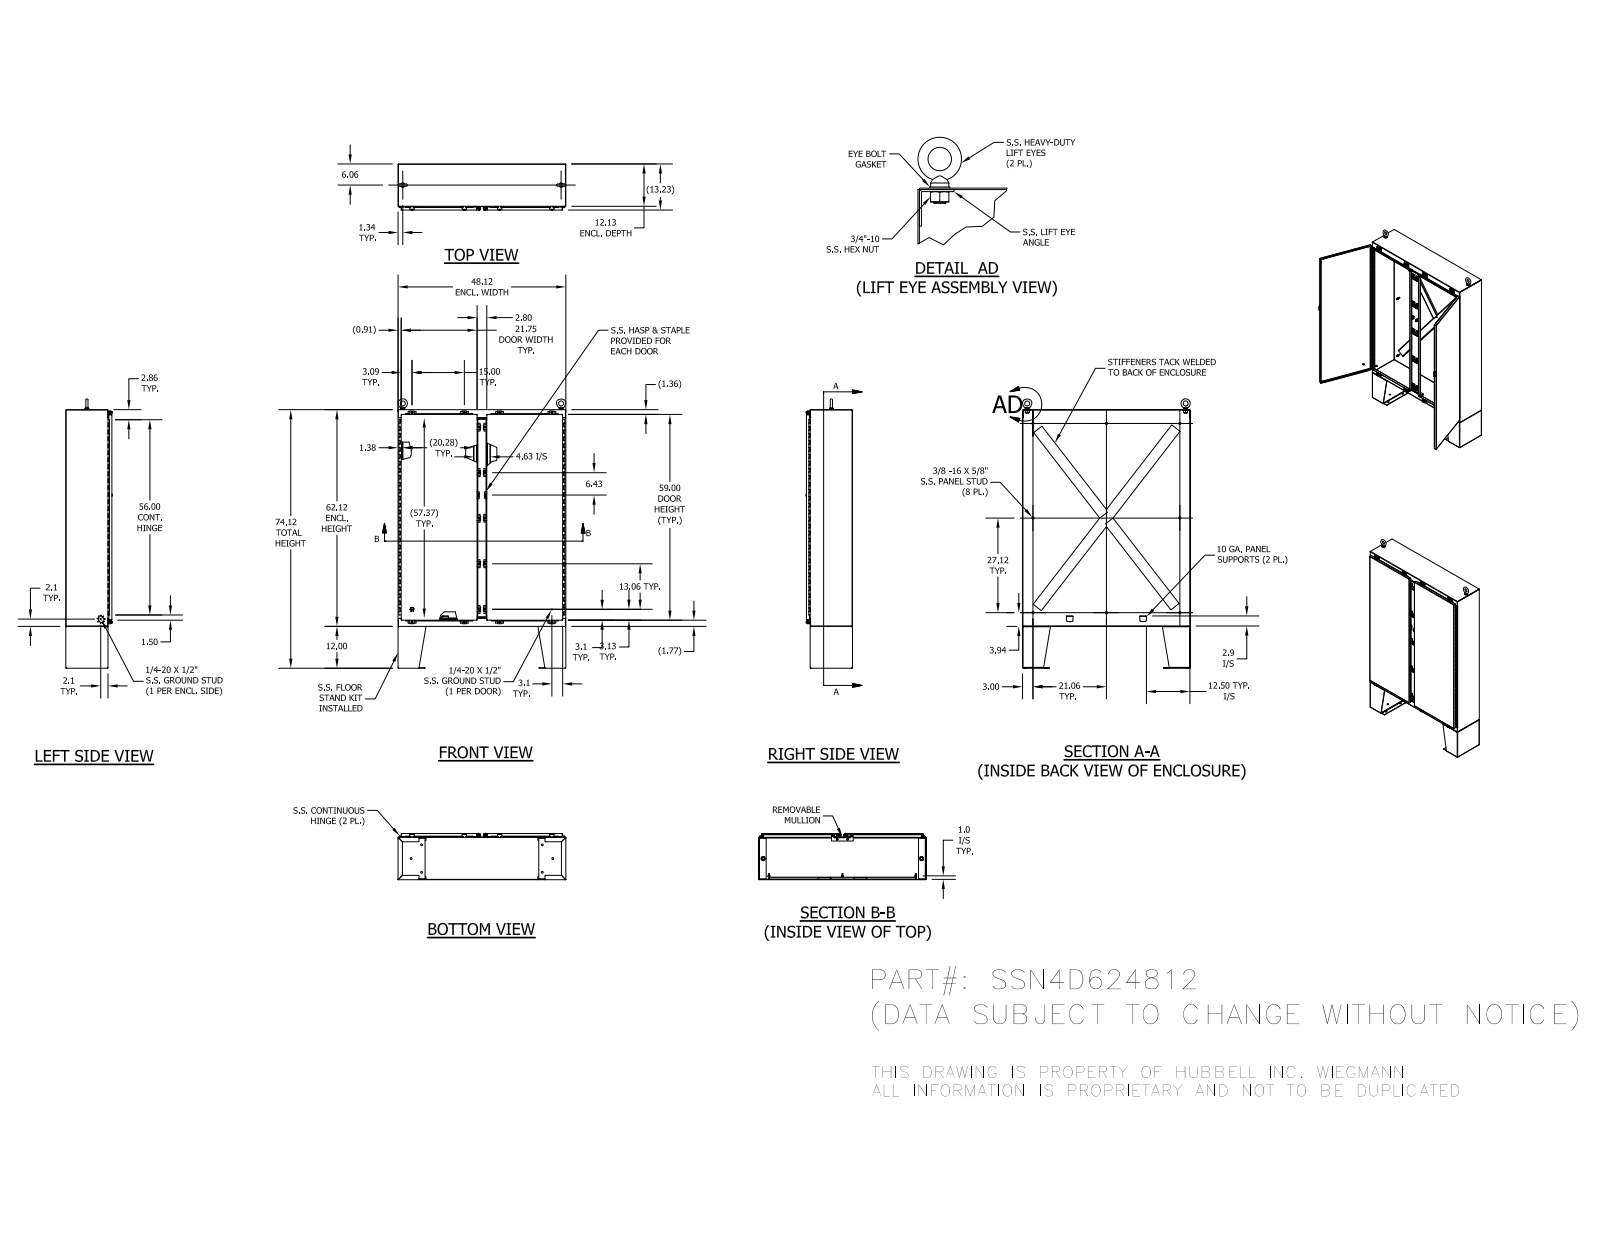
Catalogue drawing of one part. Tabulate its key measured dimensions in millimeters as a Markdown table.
| quantity | value |
| --- | --- |
| part name | 316298_1; 38626_1; 328131-56_2; 38846_1 (+8 more) |
| STEP written by | SolidWorks 2014 (AUTOMOTIVE_DESIGN) |
| units | millimeters |
| bodies | 155 solids, 5724 faces (2328 planar, 2252 cylindrical, 1144 other) |
| overall size | 1962.1 × 1222.4 × 339.2 |
| volume | 18 190 000 mm³ |
| surface area | 15 020 000 mm² |
| round holes (diameter × count) | 2.8 × 36, 5.4 × 18, 7.1 × 18, 7.6 × 18, 14.3 × 18, 9.5 × 16, 5 × 4, 5.1 × 4, 7.9 × 4, 8 × 4, 3.6 × 2, 4 × 2 |
| round bosses / shafts (diameter × count) | 6.4 × 25, 13.2 × 18, 12.7 × 18, 8.9 × 18, 8.4 × 10, 15.9 × 8, 11.1 × 4, 8.6 × 3 |
| partial cylindrical surfaces (radius × count) | 0.8 × 202, 3.2 × 56, 3.6 × 36, 6.4 × 32, 1.6 × 28, 0.8 × 24, 2.5 × 18, 0.4 × 16 |
| main face-to-face distances | 2.4, 333.6, 331.2, 336, 1220, 305.6, 28, 1575.6, 3.2, 1222.4 |
| hole center spacings | 1520.5, 381, 22.3, 617.6, 1512.1, 1512.6, 1562.5, 1641 |
